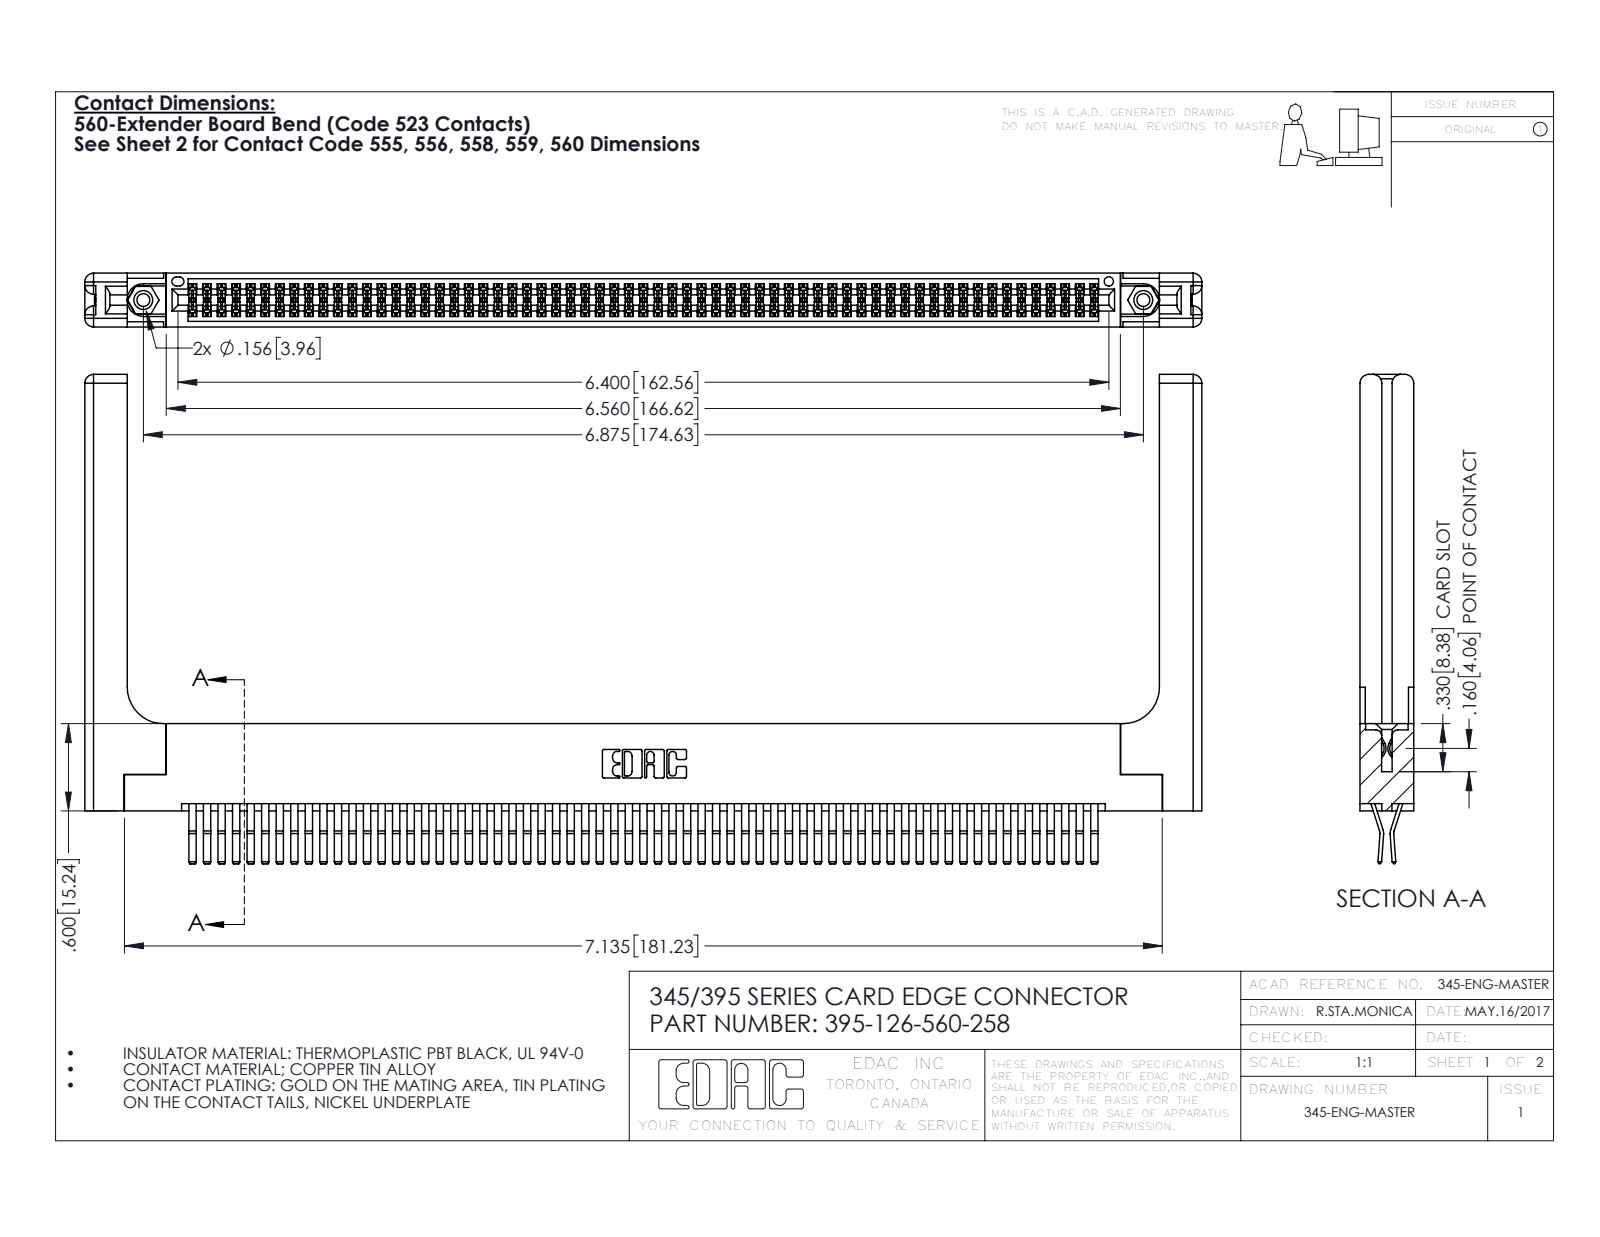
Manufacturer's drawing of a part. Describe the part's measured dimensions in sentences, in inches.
The part is named "345-220-058_345-220-058; 345-292-001_560 Tail; 345-250-001_345-250-001-102; 395-126-560-258 (+1 more)". Its 3-D file was written by "SolidWorks 2016 (CONFIG_CONTROL_DESIGN)". It is 131 solids with 6934 faces: 4386 planar, 2488 cylindrical and 60 other. Overall it measures 7.679 by 3.362 by 0.37 inches. Its volume is 1.736 cubic inches and its surface area 57.51 square inches. Round holes: 2 of diameter 0.089, 2 of diameter 0.125, 2 of diameter 0.156, 1 of diameter 0.064. Round bosses or shafts: 2 of diameter 0.155. Partial cylindrical surfaces (rounded edges, fillets, slot ends): 190 of radius 0.006, 22 of radius 0.01, 16 of radius 0.06, 6 of radius 0.007, 6 of radius 0.031, 3 of radius 0.026, 2 of radius 0.01, 2 of radius 0.014. The main face-to-face distances are 0.072, 0.298, 0.025, 0.37, 0.2, 0.098, 0.272, 0.225, 0.148, 0.15. The hole center spacings are 0.27, 6.639, 6.875.
